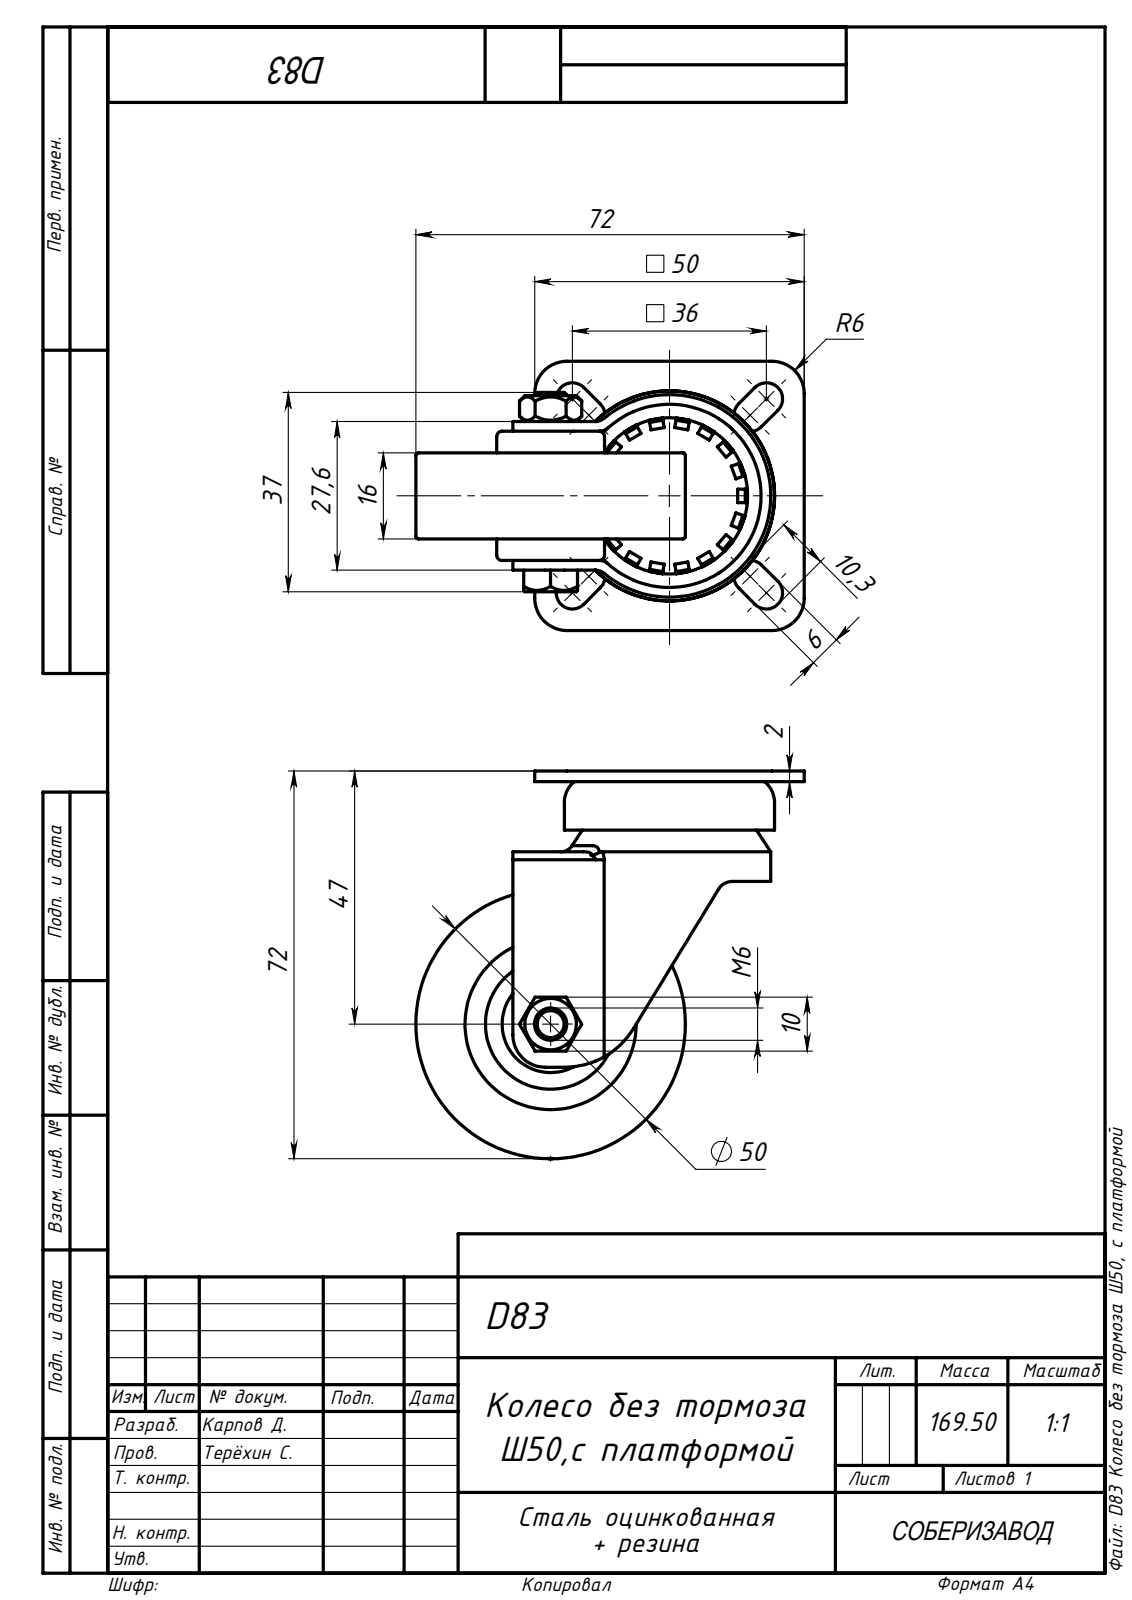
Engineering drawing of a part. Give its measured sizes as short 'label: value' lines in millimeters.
name: D83 Опора_00; D83 Колесо_00; D83 Подпишпиковый узел_00; D83 Гайка_00 (+2 more)
written by: SolidWorks 2021 (AUTOMOTIVE_DESIGN)
unit: mm
bodies: 5 solids, 283 faces (164 planar, 62 cylindrical, 57 other)
size: 72.04 × 72 × 50
volume: 47 961 mm³; area: 27 806 mm²
holes: 1× ⌀5, 1× ⌀6.2, 1× ⌀12.5, 1× ⌀18, 1× ⌀37
bosses: 1× ⌀50, 1× ⌀39, 1× ⌀29, 1× ⌀25, 1× ⌀20, 1× ⌀10, 1× ⌀6
rounds: 9× R3, 5× R6, 4× R1.5, 2× R2, 2× R2.5, 1× R15, 1× R17, 1× R18.8
face distances: 4, 16, 2, 15, 13, 1.8, 5.8, 20, 25.8, 21.8
